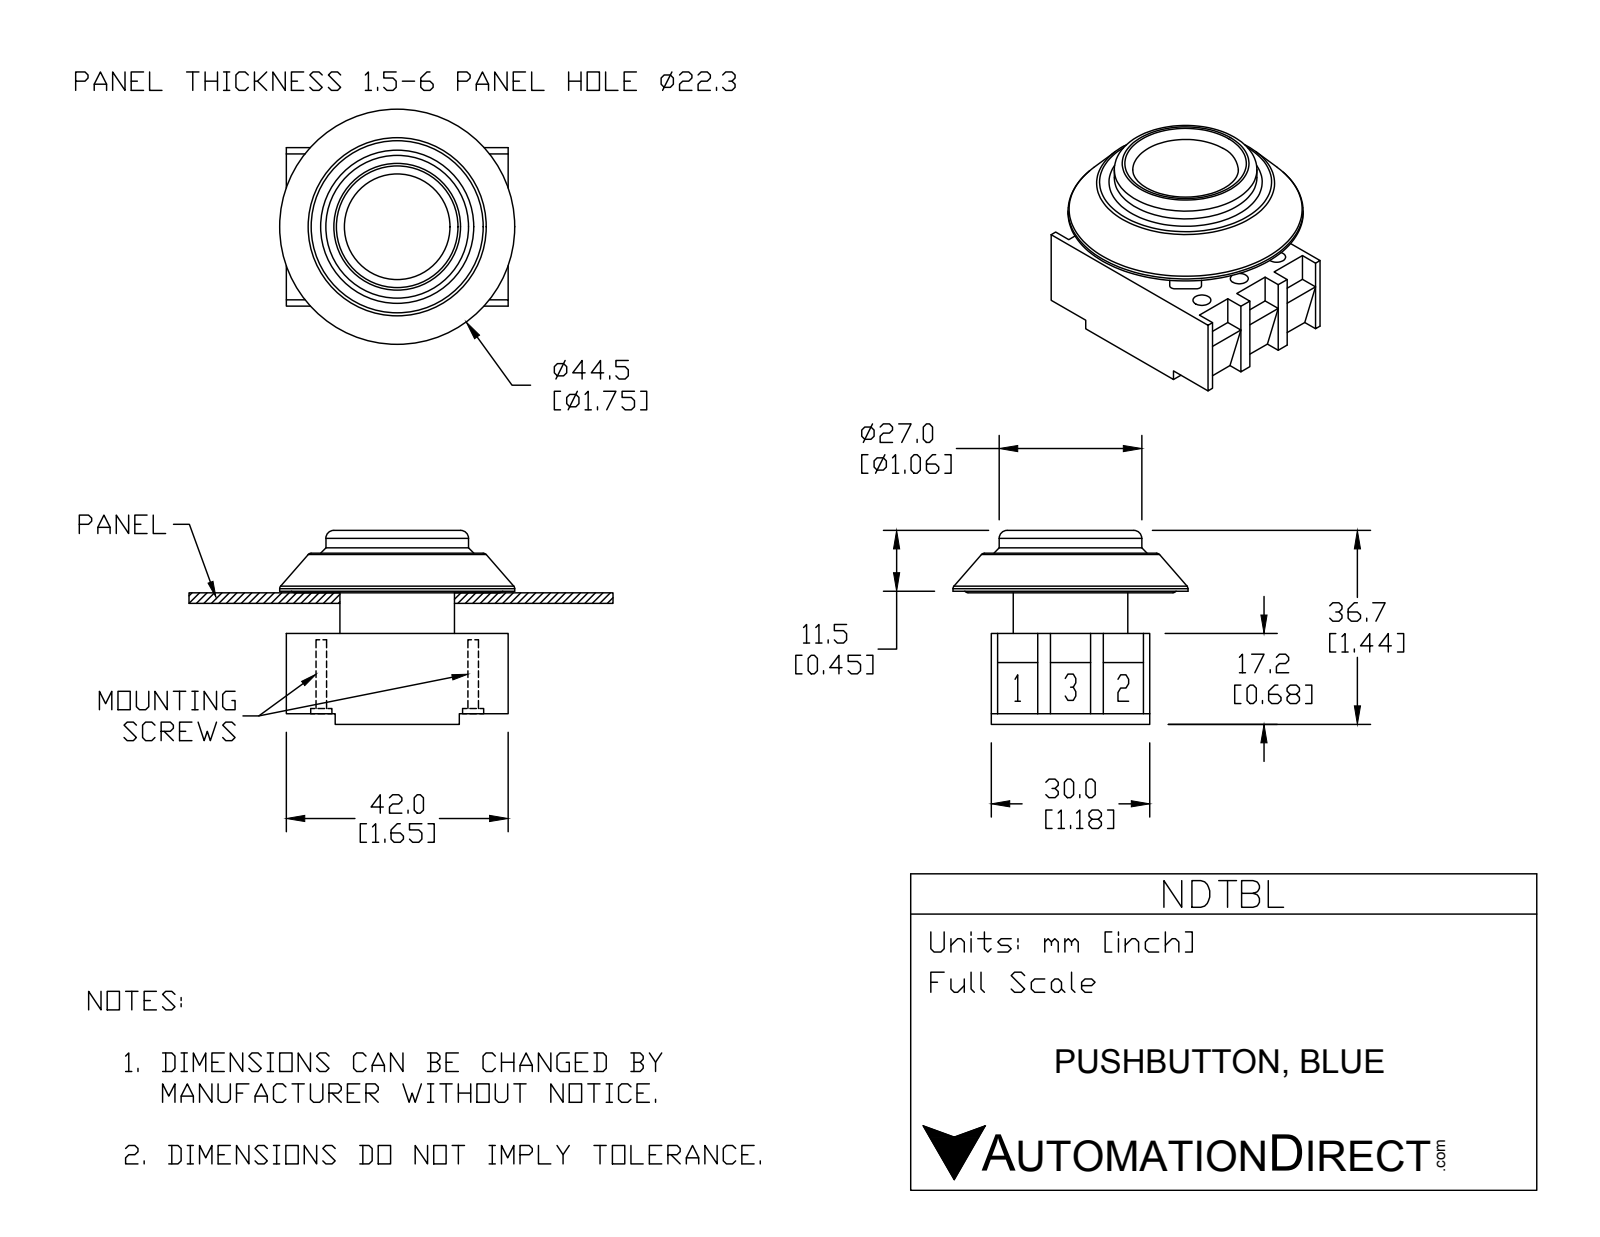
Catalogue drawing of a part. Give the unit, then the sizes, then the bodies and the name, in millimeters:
Units: millimetres
Overall size (bounding box): 44.5 × 44.5 × 36.7
Round holes (diameter × count): ⌀3.4 ×6, ⌀5 ×6, ⌀12.5 ×1
Round bosses / shafts (diameter × count): ⌀4.6 ×2, ⌀4 ×2, ⌀44.5 ×1, ⌀27 ×1, ⌀21.7 ×1
Partial cylindrical surfaces — rounded edges, fillets, slot ends (radius × count): R1 ×8, R8.7 ×5, R11 ×1
Main face-to-face distances: 7.2, 15.2, 30, 10, 8, 7.5, 7.7, 10.3, 18, 23.2
Hole centre spacings: 10, 17.52, 30.45, 28.76, 14.38, 20, 35.03
Volume: 25 120 mm³ · Surface area: 16 719 mm²
Bodies: 7 solids, 217 faces (127 planar, 65 cylindrical, 25 other)
Part name (STEP PRODUCT): NDTBL
STEP written by: SolidWorks 2015 (AUTOMOTIVE_DESIGN)
